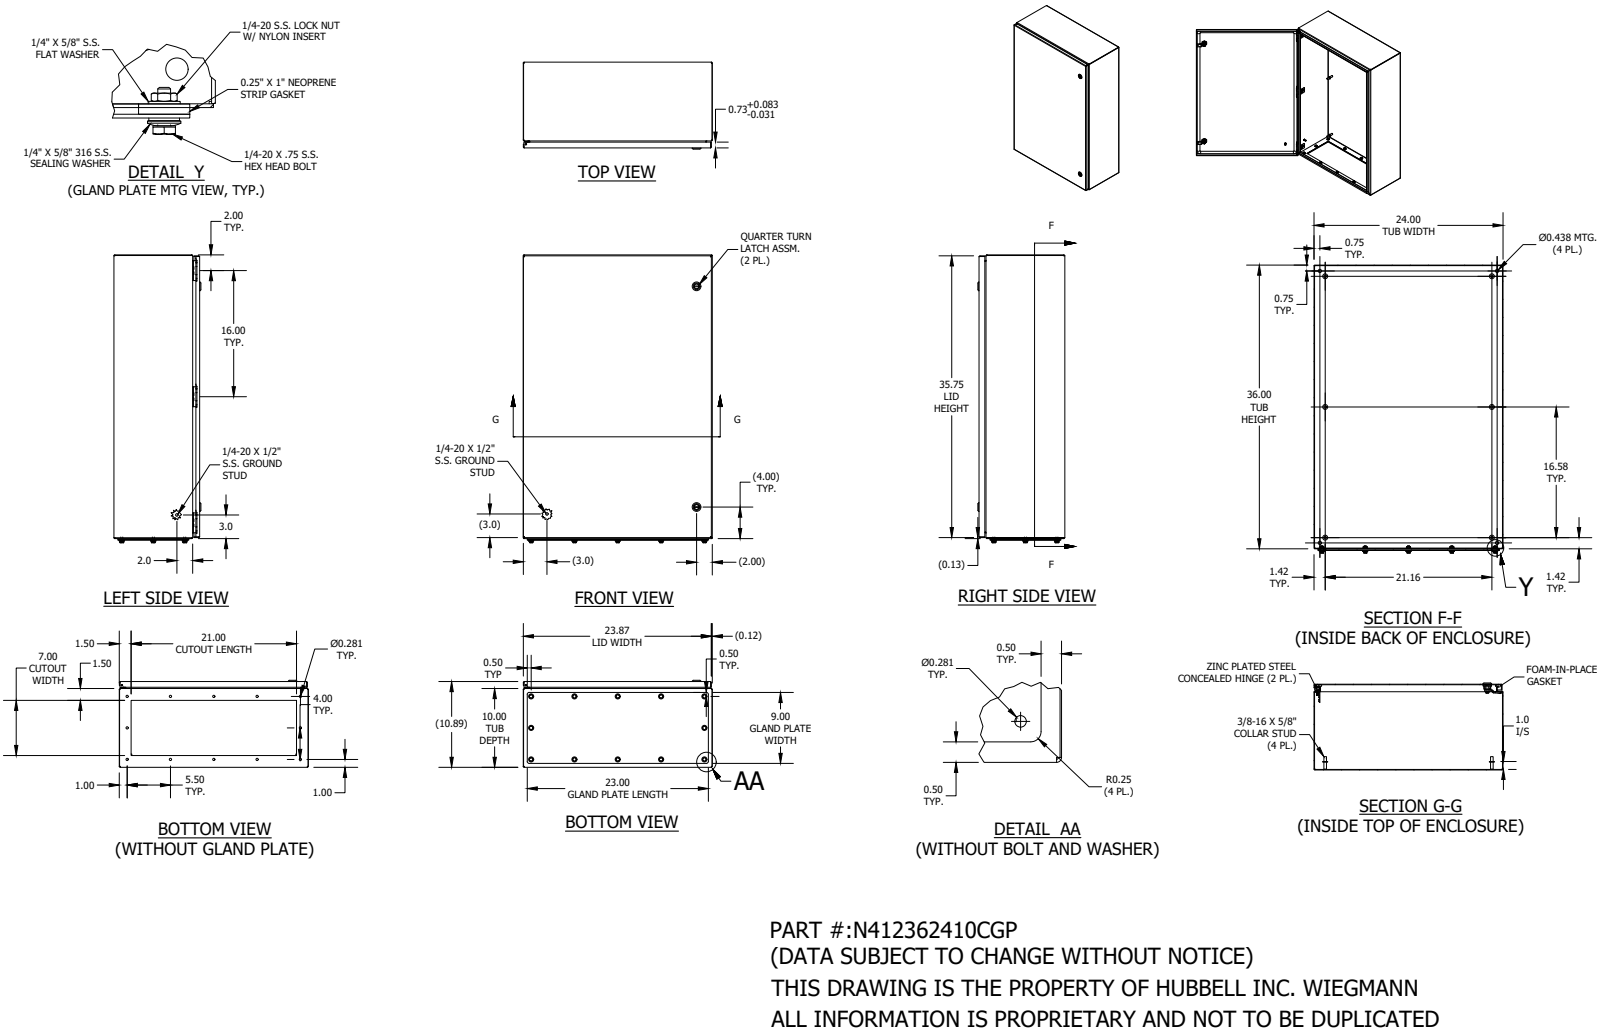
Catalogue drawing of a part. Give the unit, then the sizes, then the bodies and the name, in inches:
Units: inches
Overall size (bounding box): 36.519 × 24 × 11.044
Round holes (diameter × count): ⌀0.281 ×14, ⌀0.16 ×12, ⌀0.211 ×12, ⌀0.29 ×12, ⌀0.275 ×9, ⌀0.35 ×9, ⌀0.188 ×7, ⌀0.093 ×6, ⌀0.167 ×6, ⌀0.235 ×6, ⌀0.235 ×6, ⌀0.437 ×4
Round bosses / shafts (diameter × count): ⌀0.25 ×26, ⌀0.625 ×16, ⌀0.65 ×12, ⌀0.6 ×12, ⌀0.438 ×12, ⌀0.36 ×6, ⌀0.33 ×6, ⌀0.32 ×6
Partial cylindrical surfaces — rounded edges, fillets, slot ends (radius × count): R0.012 ×56, R0.05 ×38, R0.02 ×21, R0.047 ×20, R0.121 ×20, R0.125 ×12, R0.13 ×12, R0.157 ×9
Main face-to-face distances: 0.074, 10.812, 10.738, 10.886, 0.074, 23.926, 36.13, 23.852, 24, 36.056
Hole centre spacings: 4, 16, 5.5, 8, 0.66, 11, 16.002, 22.361
Volume: 273 in³ · Surface area: 6 893 in²
Bodies: 107 solids, 3129 faces (1219 planar, 976 cylindrical, 934 other)
Part name (STEP PRODUCT): N412362410CGP
STEP written by: SolidWorks 2019 (AUTOMOTIVE_DESIGN)
